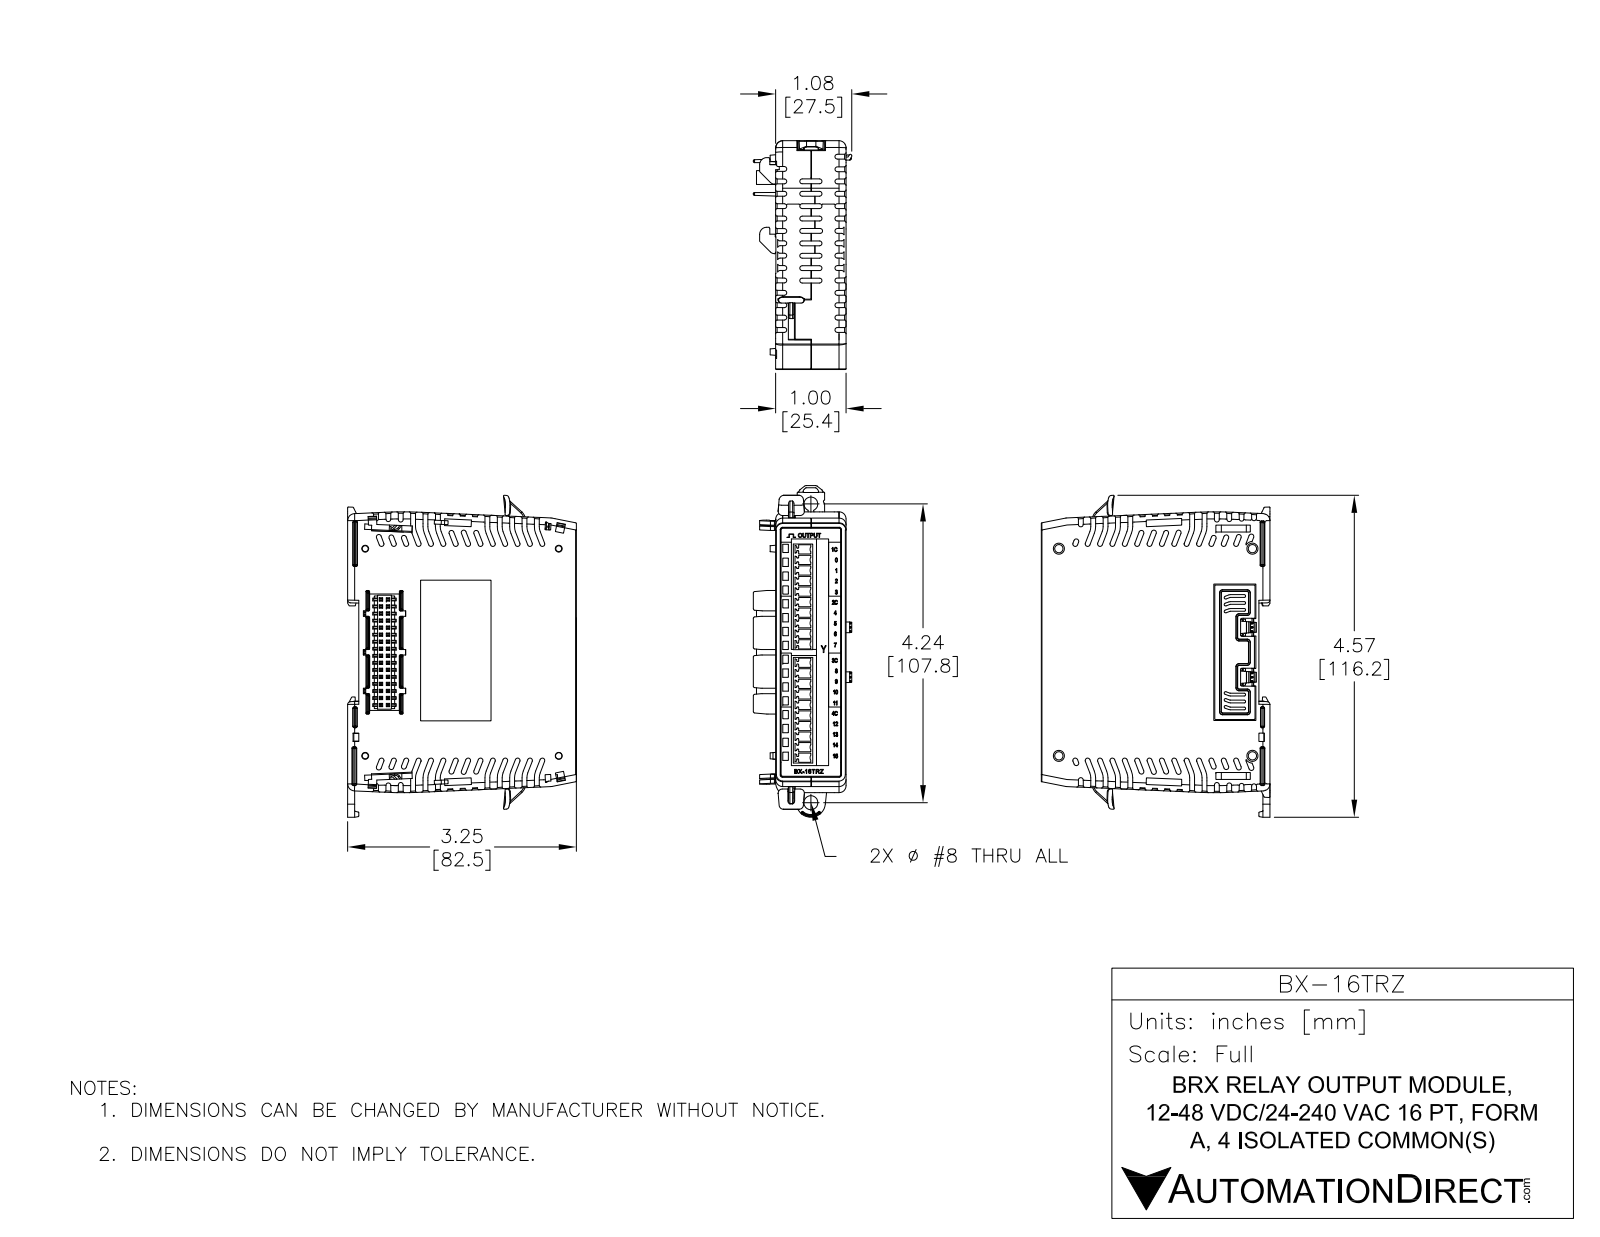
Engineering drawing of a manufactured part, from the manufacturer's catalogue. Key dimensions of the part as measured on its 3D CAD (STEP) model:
Part name (STEP PRODUCT): BX-16TRZ red door c comb1 fXT
STEP written by: SolidWorks 2017 (AUTOMOTIVE_DESIGN)
Units: inches
Bodies: 14 solids, 3880 faces (2890 planar, 477 cylindrical, 513 other)
Overall size (bounding box): 4.586 × 3.25 × 1.4
Volume: 11.58 in³ · Surface area: 72.2 in²
Round holes (diameter × count): ⌀0.047 ×2, ⌀0.065 ×2, ⌀0.118 ×2, ⌀0.118 ×2, ⌀0.199 ×1
Round bosses / shafts (diameter × count): ⌀0.062 ×2, ⌀0.059 ×2
Partial cylindrical surfaces — rounded edges, fillets, slot ends (radius × count): R0.008 ×101, R0.01 ×46, R0.005 ×24, R0.02 ×22, R0.062 ×20, R0.117 ×14, R0.039 ×13, R0.01 ×12
Main face-to-face distances: 1, 3.211, 3.22, 0.039, 0.475, 0.157, 3.053, 3.063, 0.1, 0.052
Hole centre spacings: 0.1, 0.824, 0.919, 1.3, 2.093, 2.193, 2.585, 2.617
